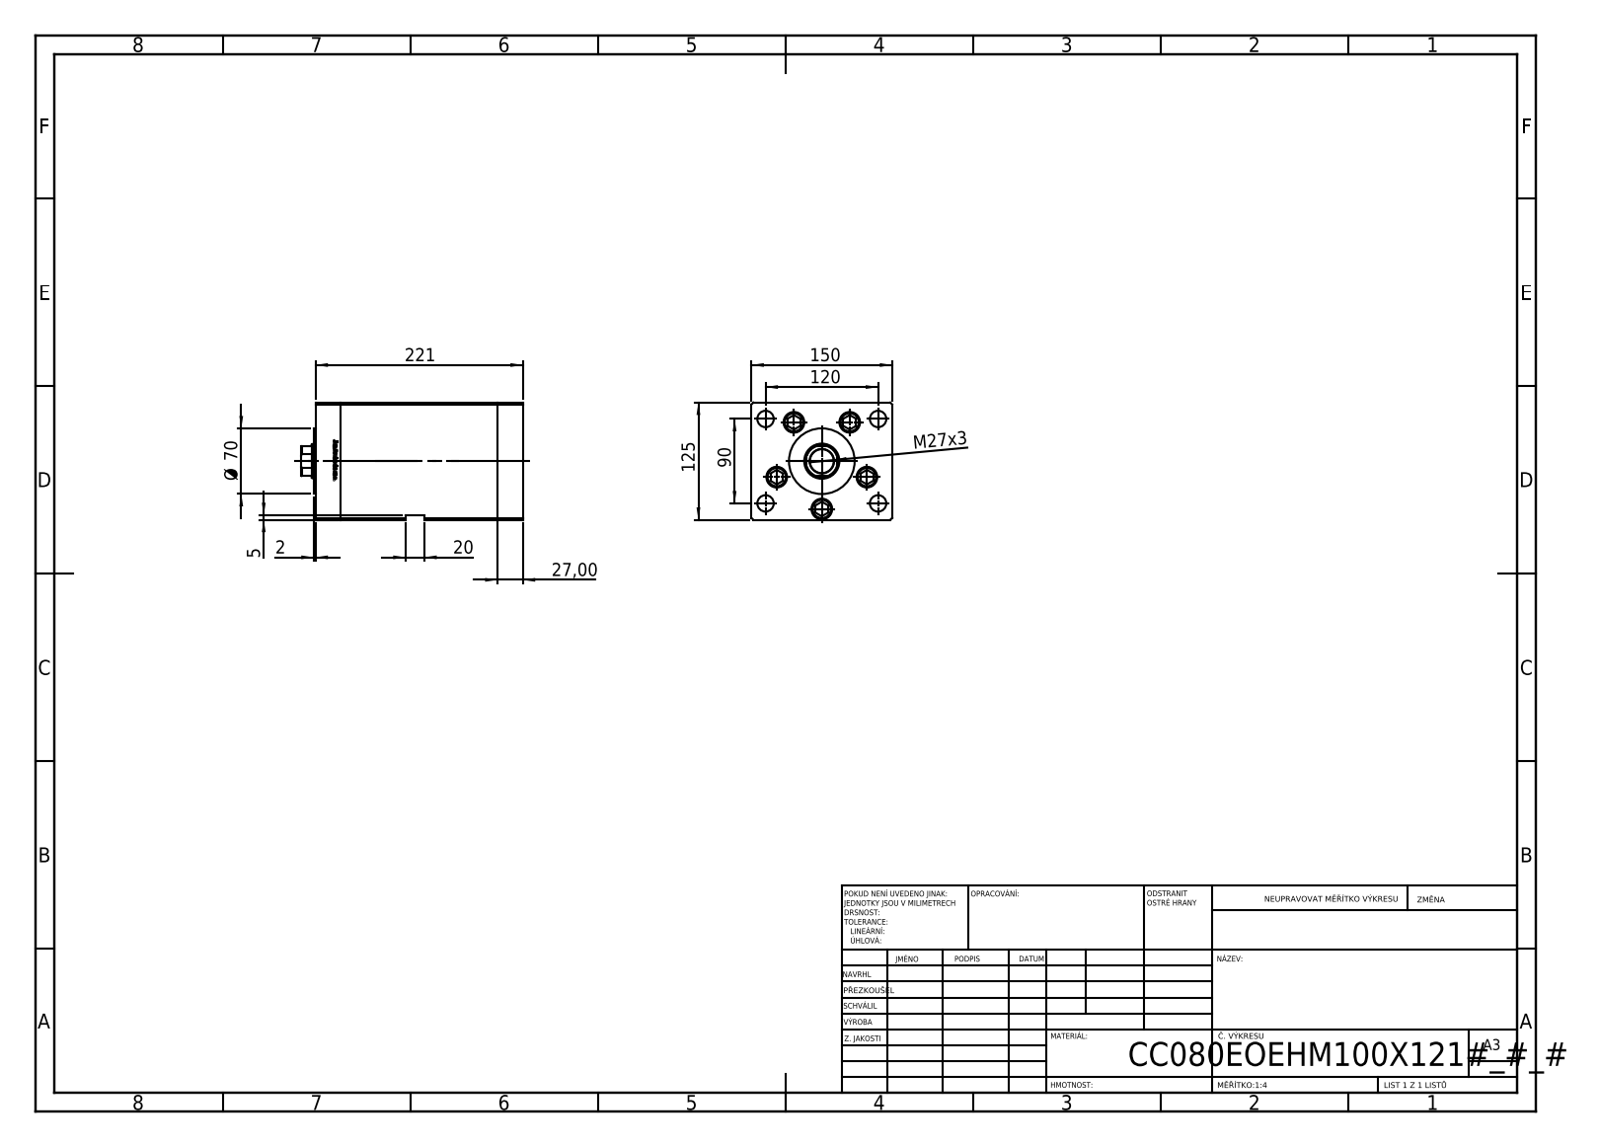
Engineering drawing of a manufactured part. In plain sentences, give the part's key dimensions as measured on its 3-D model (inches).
The part is named "V220C_VC_E; ALLEN BOLT; V220C_FRONT_E; V220C BACK_E (+1 more)". Its 3-D file was written by "SolidWorks 2019 (CONFIG_CONTROL_DESIGN)". It is 14 solids with 1214 faces: 475 planar, 165 cylindrical and 574 other. Overall it measures 9.291 by 5.906 by 4.921 inches. Its volume is 208.8 cubic inches and its surface area 615.3 square inches. Round holes: 9 of diameter 0.689, 5 of diameter 0.866, 4 of diameter 0.669, 4 of diameter 0.906, 2 of diameter 0.079, 2 of diameter 0.518, 1 of diameter 1.004, 1 of diameter 1.417, 1 of diameter 1.476. Round bosses or shafts: 5 of diameter 0.827, 5 of diameter 0.315, 1 of diameter 3.15, 1 of diameter 2.756. Partial cylindrical surfaces (rounded edges, fillets, slot ends): 2 of radius 0.037, 1 of radius 0.689. The main face-to-face distances are 1.063, 7.638, 6.575, 4.921, 5.906, 1.319, 0.256, 8.701, 6.319, 7.382. The hole center spacings are 2.008, 2.953, 1.198, 1.2, 2.319, 2.374, 2.411, 2.486.
